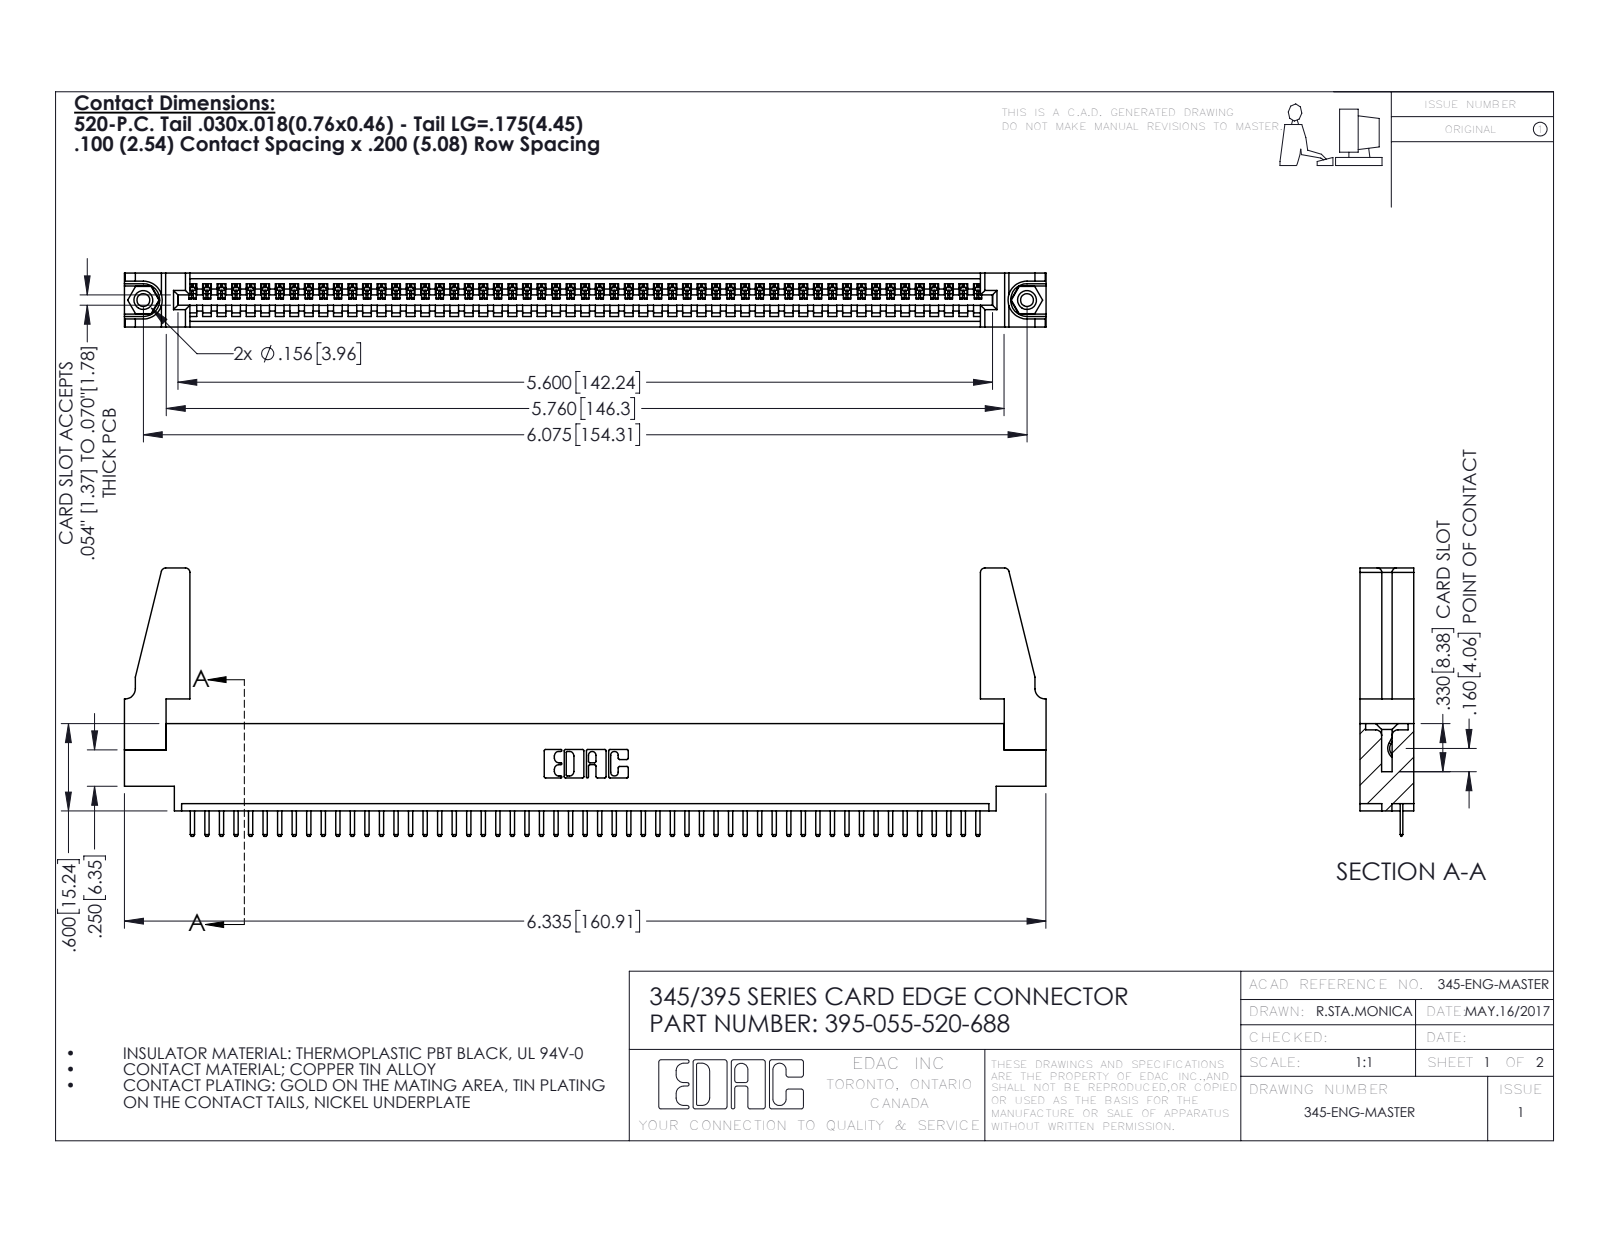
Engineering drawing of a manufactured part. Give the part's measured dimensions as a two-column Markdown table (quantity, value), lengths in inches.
| quantity | value |
| --- | --- |
| part name | 345-220-078_345-220-088; 345-292-001_345-293-120; 395-055-520-688; 345 Part_0.170 Offset - 0.156 Dia-TH (+1 more) |
| STEP written by | SolidWorks 2016 (CONFIG_CONTROL_DESIGN) |
| units | inches |
| bodies | 60 solids, 3664 faces (2466 planar, 1182 cylindrical, 16 other) |
| overall size | 6.336 × 1.845 × 0.37 |
| volume | 1.121 in³ |
| surface area | 35.66 in² |
| round holes (diameter × count) | 0.089 × 2, 0.125 × 2, 0.156 × 2, 0.064 × 1 |
| round bosses / shafts (diameter × count) | 0.155 × 2 |
| partial cylindrical surfaces (radius × count) | 0.01 × 112, 0.006 × 110, 0.01 × 22, 0.03 × 8, 0.007 × 6, 0.031 × 6, 0.026 × 3, 0.031 × 2 |
| main face-to-face distances | 0.072, 0.37, 0.298, 0.2, 0.098, 0.272, 0.025, 0.225, 0.072, 0.175 |
| hole center spacings | 0.27, 5.839, 6.075 |
